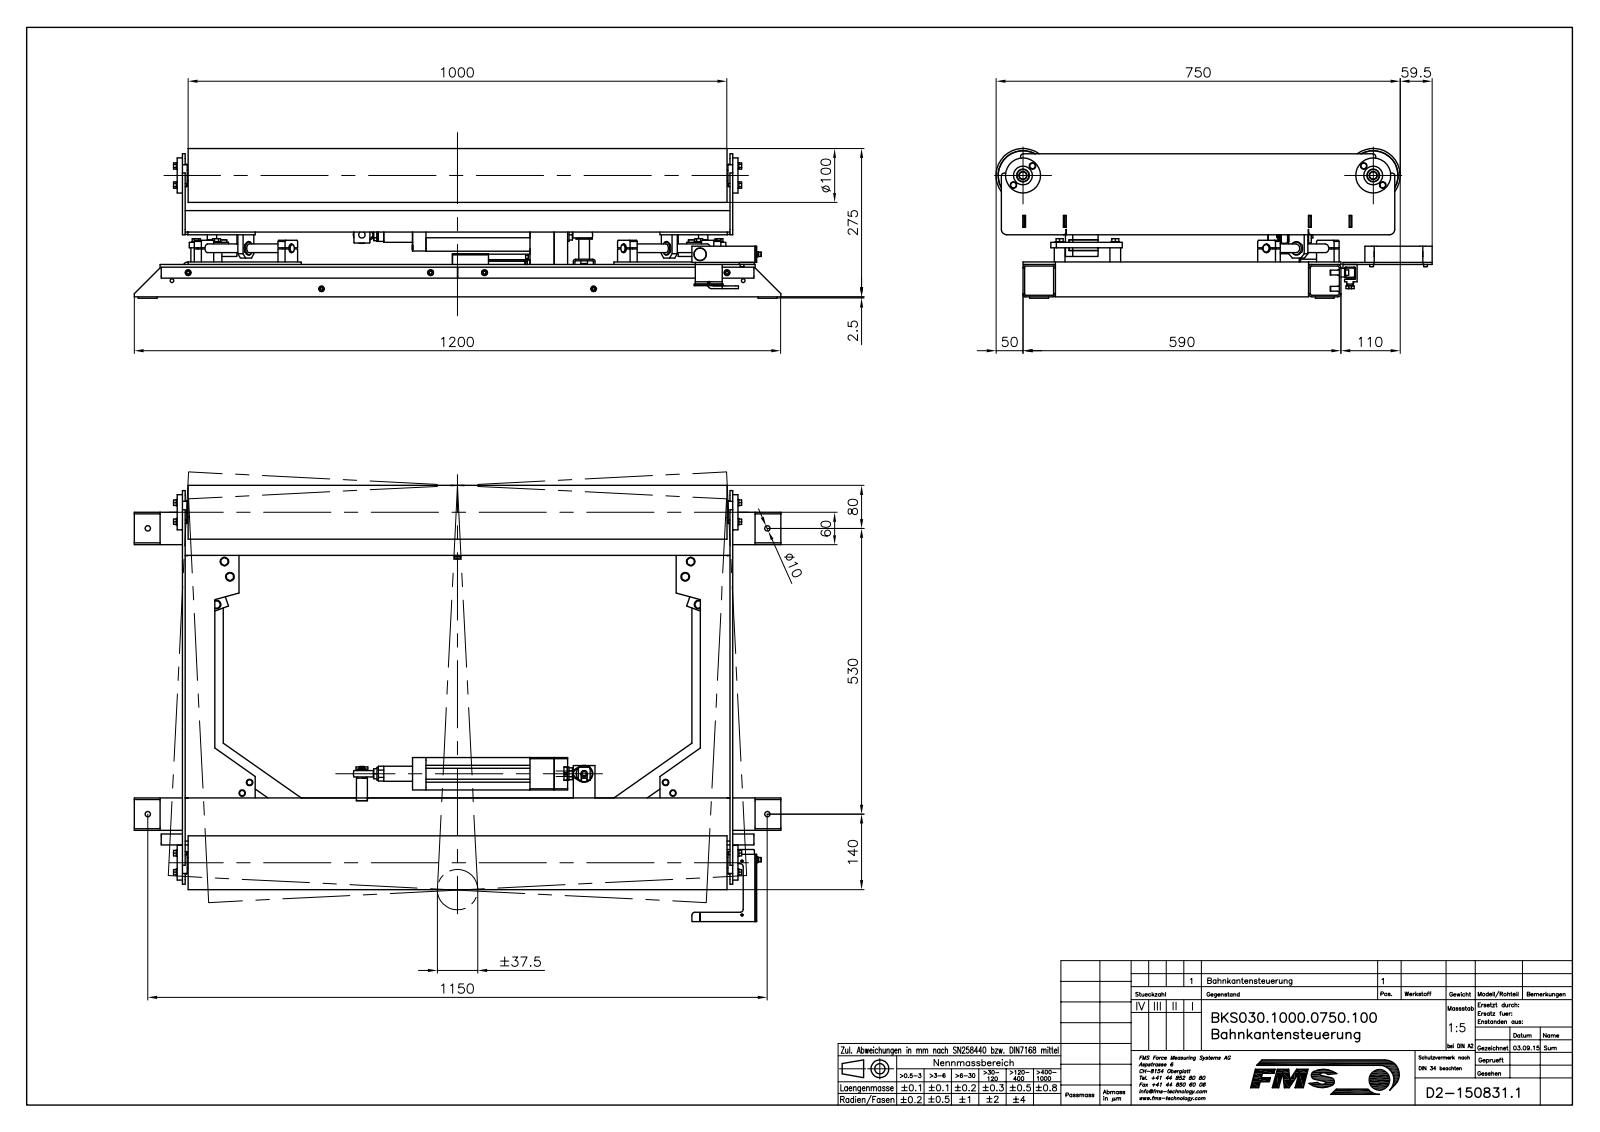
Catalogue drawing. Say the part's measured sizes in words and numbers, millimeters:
The part is named "K1508311; K1508312; K1508315; K1508314 (+8 more)". Its 3-D file was written by "Mechanical Desktop 2009 (CONFIG_CONTROL_DESIGN)". It is 160 solids with 2672 faces: 1281 planar, 1013 cylindrical and 378 other. Overall it measures 1200 by 809.5 by 277.5 millimeters. Its volume is 9 623 000 cubic millimeters and its surface area 4 763 000 square millimeters. Round holes: 25 of diameter 5.15, 19 of diameter 7, 12 of diameter 4.3, 12 of diameter 11, 10 of diameter 8.4, 9 of diameter 6.4, 8 of diameter 10, 6 of diameter 3.42, 6 of diameter 16, 4 of diameter 2.6, 4 of diameter 3.2, 4 of diameter 5.5. Round bosses or shafts: 22 of diameter 6, 16 of diameter 10, 13 of diameter 8, 12 of diameter 16, 11 of diameter 12, 10 of diameter 9, 10 of diameter 4, 8 of diameter 20. Partial cylindrical surfaces (rounded edges, fillets, slot ends): 22 of radius 1, 19 of radius 2, 19 of radius 5, 16 of radius 4, 8 of radius 3, 8 of radius 6, 6 of radius 10, 4 of radius 0.4. The main face-to-face distances are 3, 5, 60, 57, 530, 37, 63, 100, 120, 157. The hole center spacings are 95, 24, 190, 30, 25, 57.28, 97.98, 97.99.
